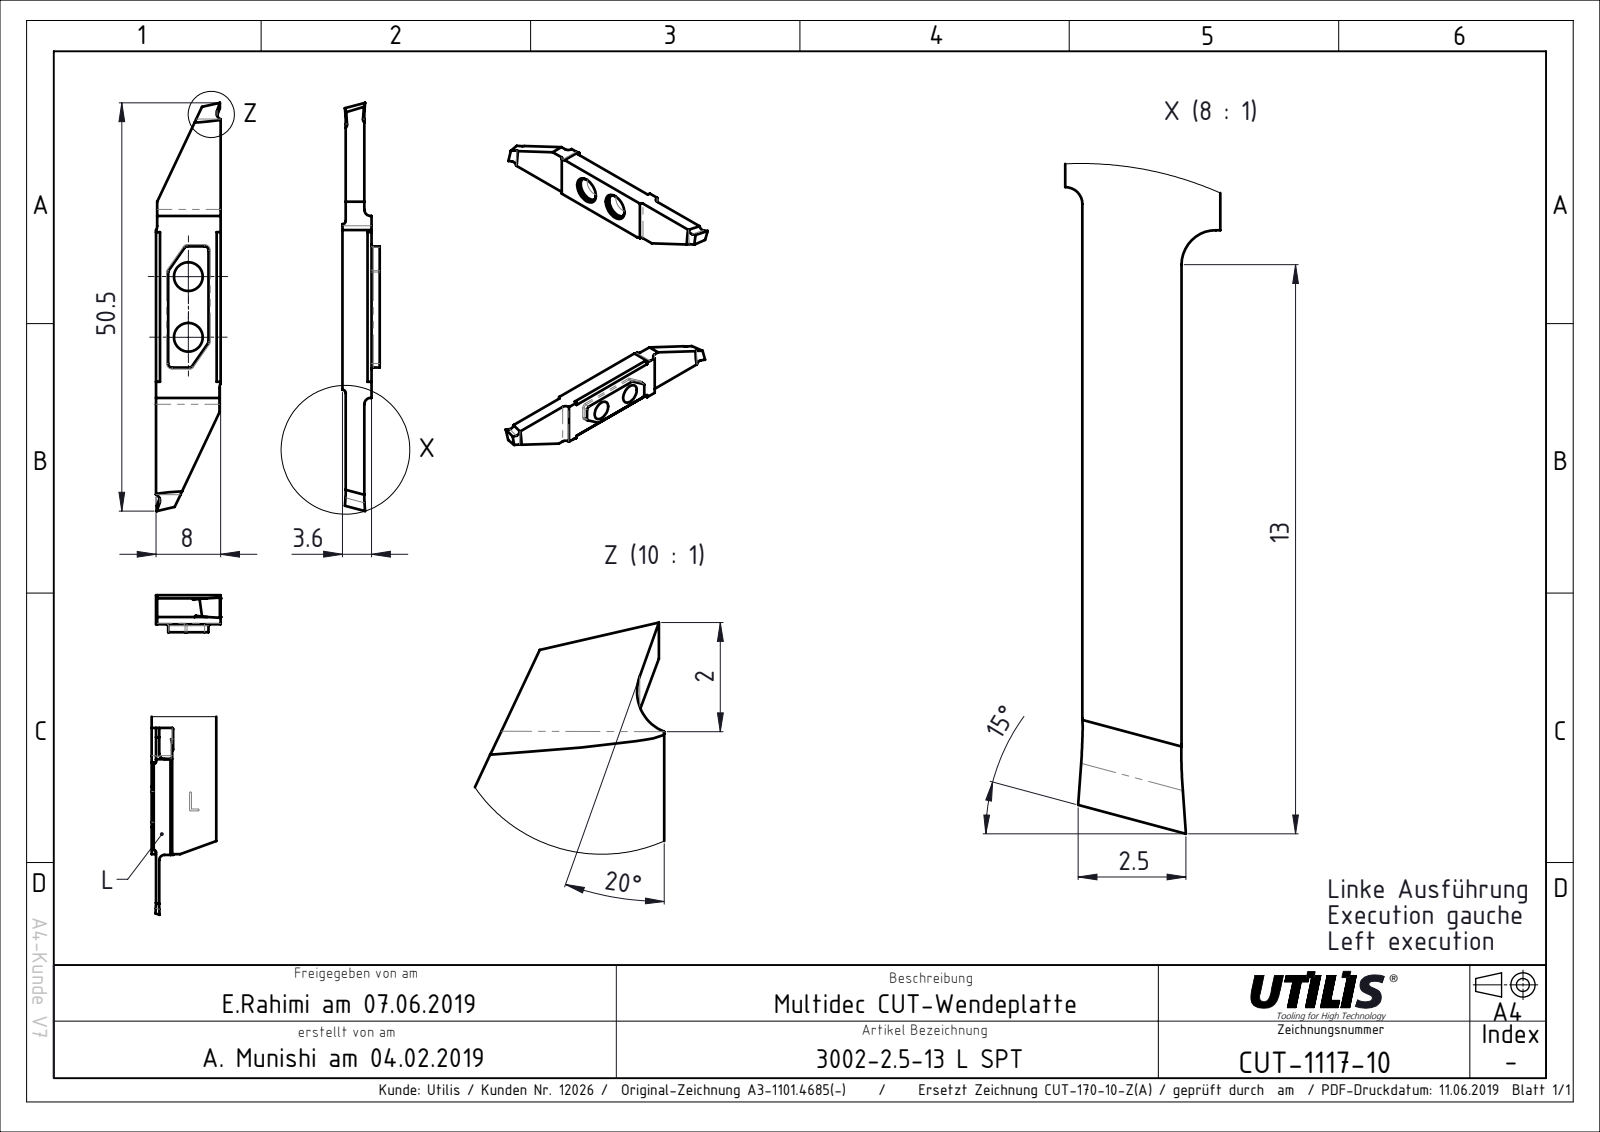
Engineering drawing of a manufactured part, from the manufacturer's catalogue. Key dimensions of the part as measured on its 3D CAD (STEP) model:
Part name (STEP PRODUCT): CUT-1117; ASME Y14.5
STEP written by: FormatWorks Professional (AP242_MANAGED_MODEL_BASED_3D_ENGINEERING_MIM_LF)
Units: millimetres
Bodies: 1 solid, 38 faces (28 planar, 10 cylindrical, 0 other)
Overall size (bounding box): 50.5 × 8 × 3.6
Volume: 906 mm³ · Surface area: 1 002 mm²
Round holes (diameter × count): ⌀3.55 ×2
Partial cylindrical surfaces — rounded edges, fillets, slot ends (radius × count): R0.4 ×2, R0.8 ×2, R1 ×2
Main face-to-face distances: 0.41, 3.6, 3.19, 2.69, 2.28, 0.91, 8, 18.09, 7.85, 7.7
Hole centre spacings: 7.5
